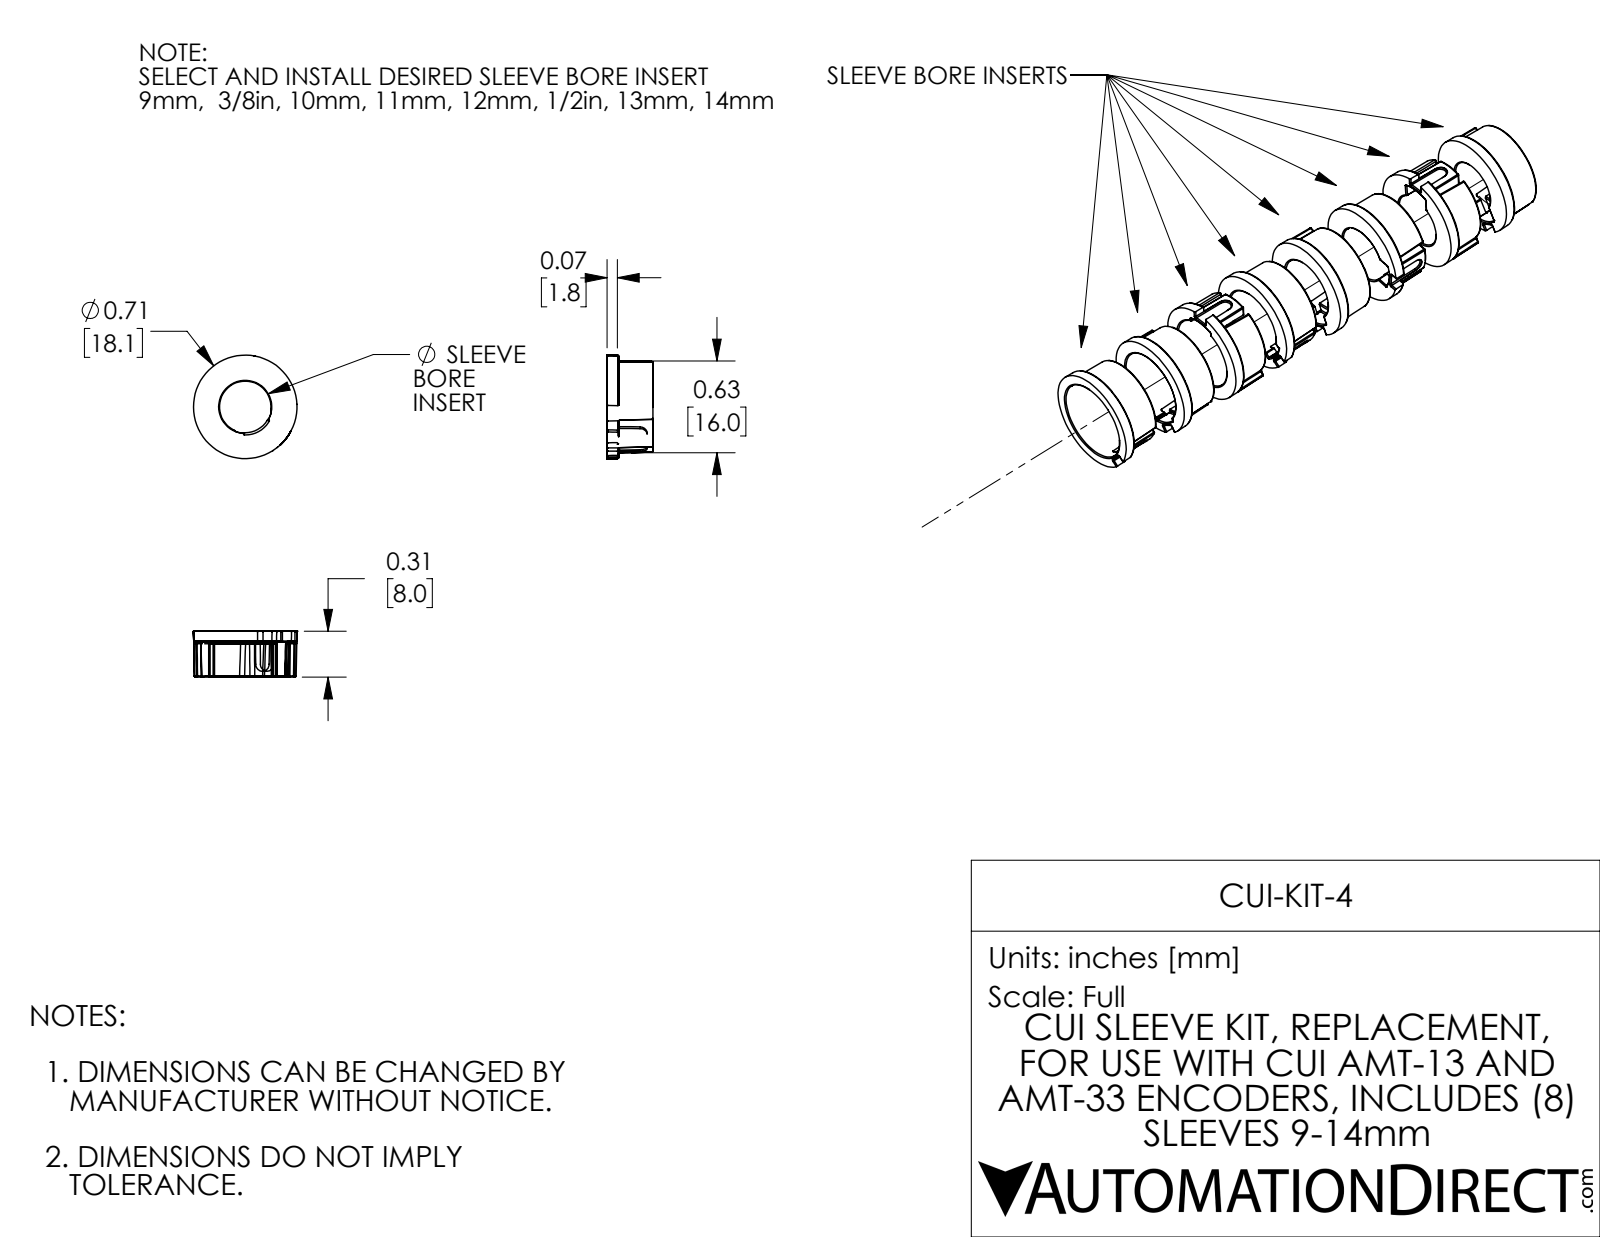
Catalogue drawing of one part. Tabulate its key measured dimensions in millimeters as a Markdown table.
| quantity | value |
| --- | --- |
| part name | CUI-KIT-4 |
| STEP written by | SolidWorks 2021 (AUTOMOTIVE_DESIGN) |
| units | millimeters |
| bodies | 8 solids, 764 faces (133 planar, 144 cylindrical, 487 other) |
| overall size | 96.2 × 18.7 × 18.4 |
| volume | 6 370 mm³ |
| surface area | 8 129 mm² |
| partial cylindrical surfaces (radius × count) | 0.2 × 136, 1.3 × 8 |
| main face-to-face distances | 8, 6, 12.9, 25.6, 12.8, 38.5, 25.7, 12.9, 51, 38.2 |
